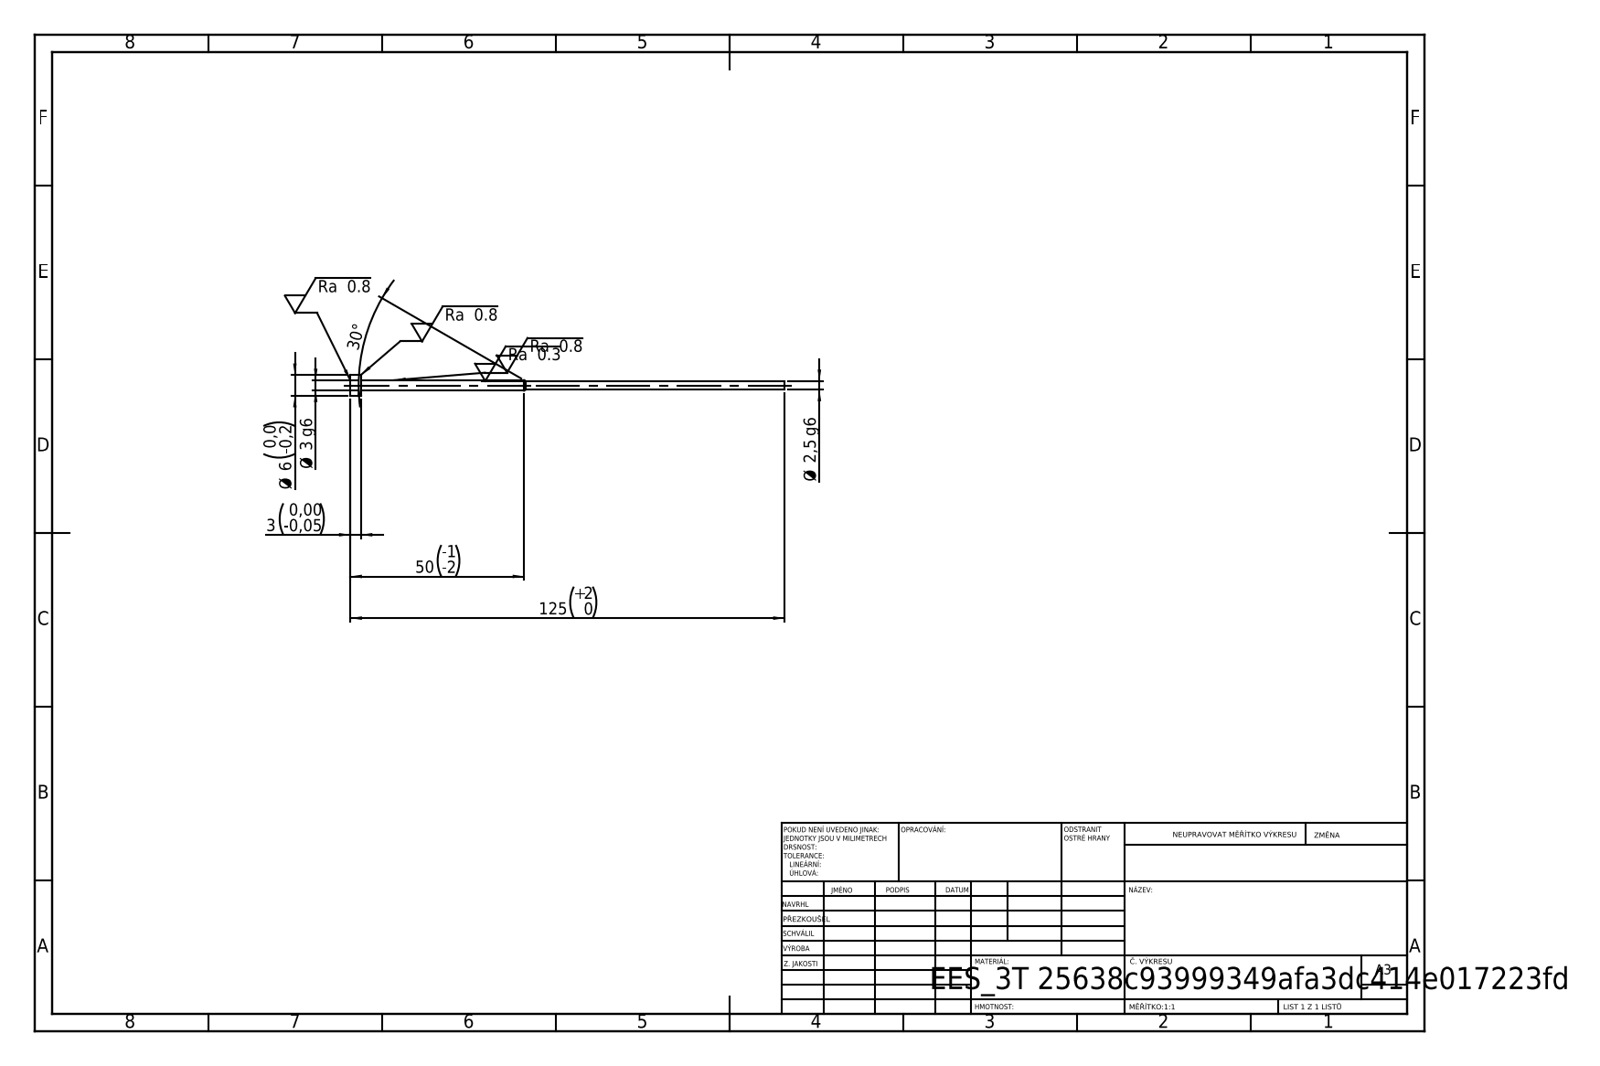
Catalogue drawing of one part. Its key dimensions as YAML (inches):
step_written_by: "SolidWorks 2019 (CONFIG_CONTROL_DESIGN)"
units: inches
bodies: {solids: 1, faces: 11, planar: 3, cylindrical: 6, other: 2}
overall_size: [4.921, 0.236, 0.236]
volume: 0.048
surface_area: 1.773
round_bosses_or_shafts:
  - {diameter: 0.236, count: 1}
  - {diameter: 0.118, count: 1}
  - {diameter: 0.098, count: 1}
face_to_face_distances: [0.118, 4.803, 4.921]
